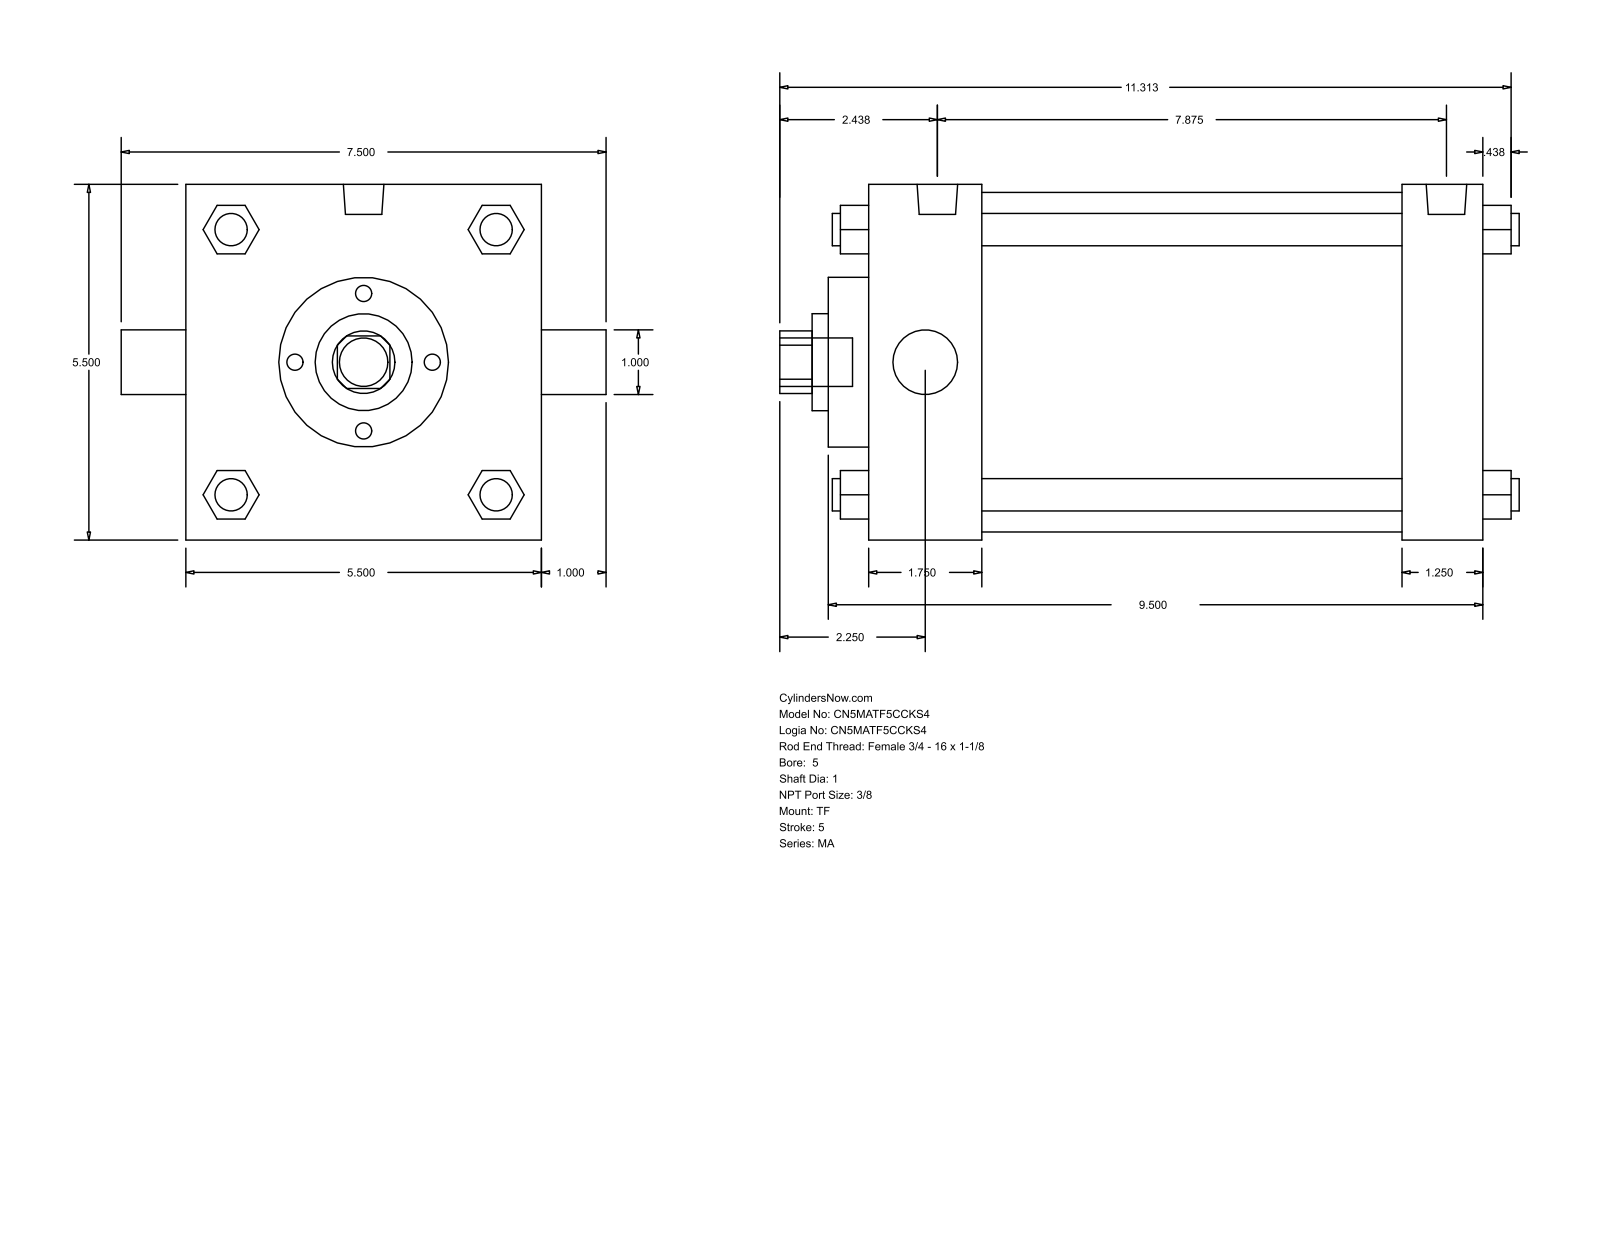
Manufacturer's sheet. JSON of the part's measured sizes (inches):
{"part_name": "MA_TF__0500_1", "step_written_by": "GSSL Pune (CONFIG_CONTROL_DESIGN)", "units": "inches", "bodies": {"solids": 0, "faces": 122, "planar": 93, "cylindrical": 29, "other": 0}, "overall_size": [11.437, 7.5, 5.5], "round_holes": [[1, 2], [1.5, 1], [2.625, 1], [5.25, 1]], "round_bosses_or_shafts": [[0.5, 4], [0.437, 3], [0.627, 2], [0.75, 1]], "partial_cylinders_radius": [[0.484, 1]], "face_to_face_distances": [5.5, 9.5, 8.25, 1.25, 1.75, 6.5, 7.75, 0.625, 2.375, 8.875]}
